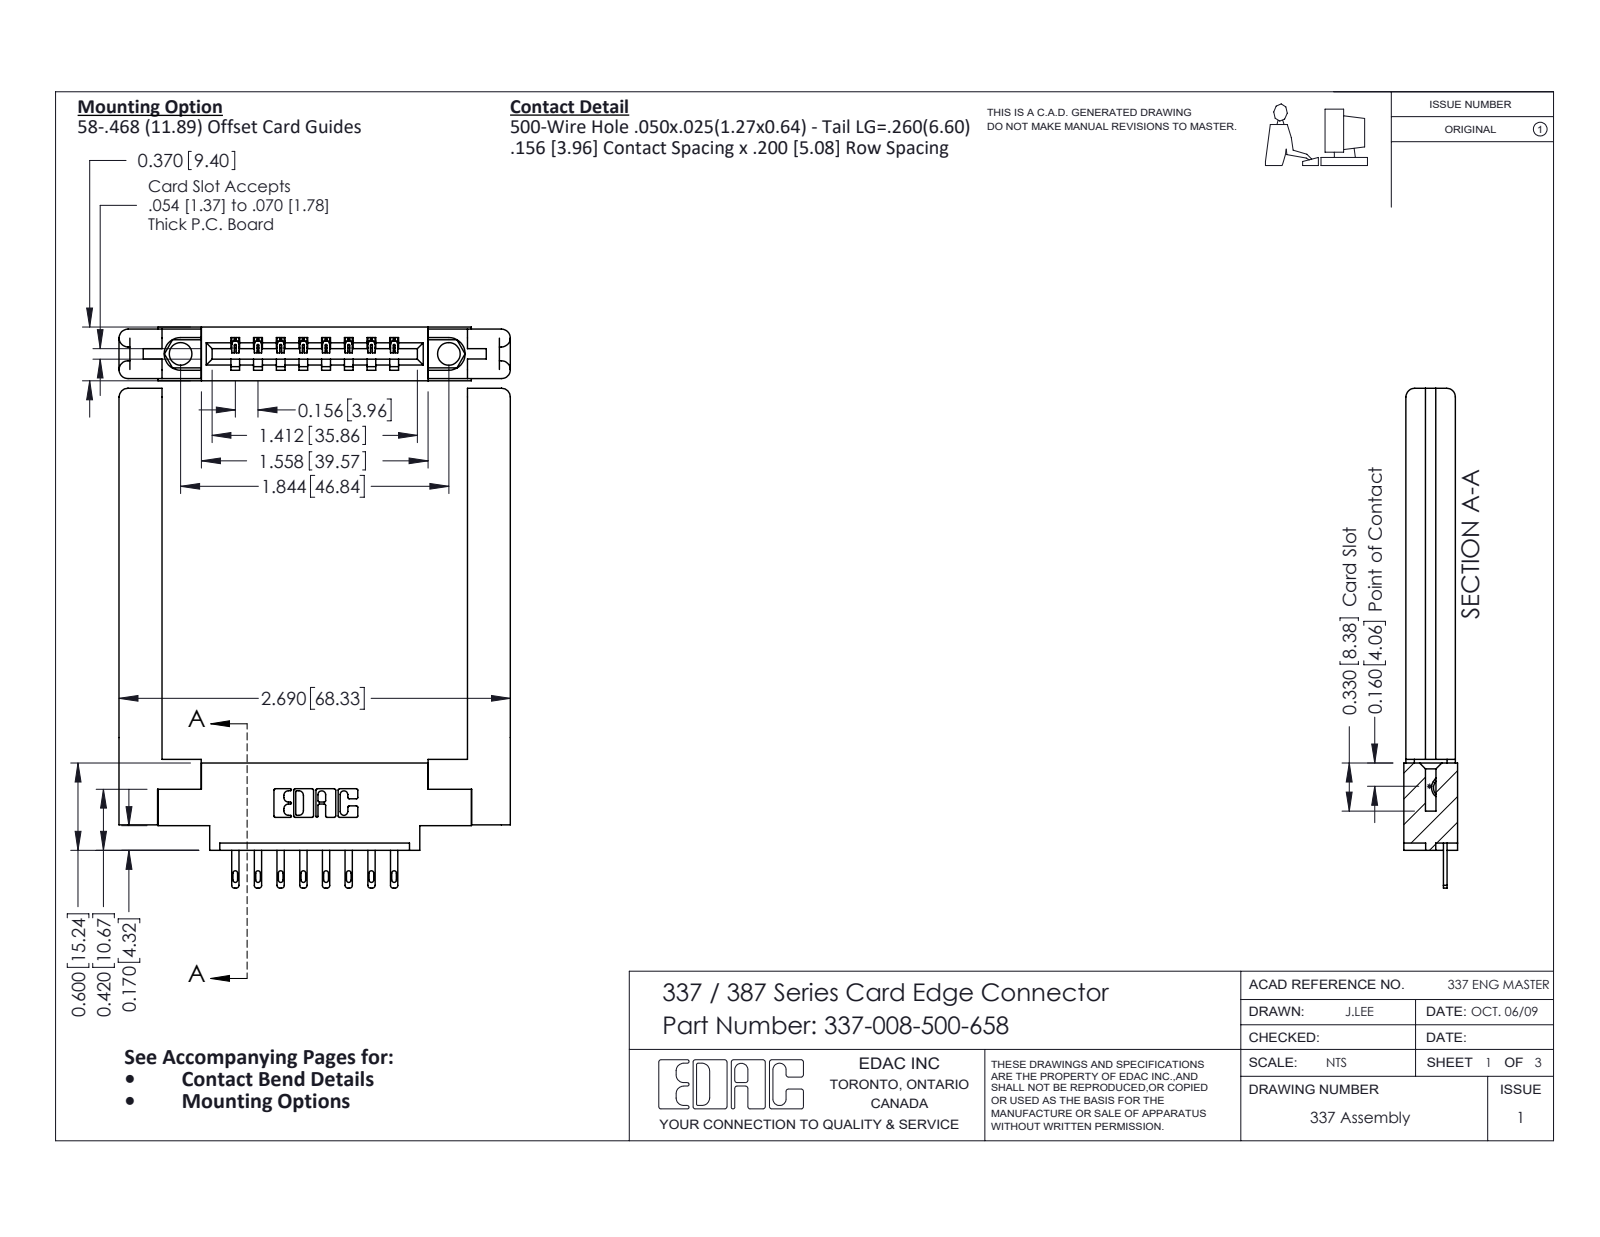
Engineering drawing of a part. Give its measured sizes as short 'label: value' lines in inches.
name: 345-292-001_345-293-100; 307-220-058; 345-250-001_345-250-001-102; 337-008-500-658 (+1 more)
written by: SolidWorks 2016 (CONFIG_CONTROL_DESIGN)
unit: in
bodies: 13 solids, 724 faces (478 planar, 222 cylindrical, 24 other)
size: 3.435 × 2.69 × 0.37
volume: 0.838 in³; area: 18.48 in²
holes: 2× ⌀0.089, 2× ⌀0.125, 2× ⌀0.156
bosses: 2× ⌀0.155
rounds: 22× R0.01, 16× R0.006, 16× R0.016, 16× R0.02, 8× R0.061, 6× R0.007, 6× R0.031, 5× R0.06
face distances: 0.355, 0.015, 0.34, 0.15, 0.135, 0.22, 0.206, 0.37, 0.148, 0.072
hole spacings: 1.844
